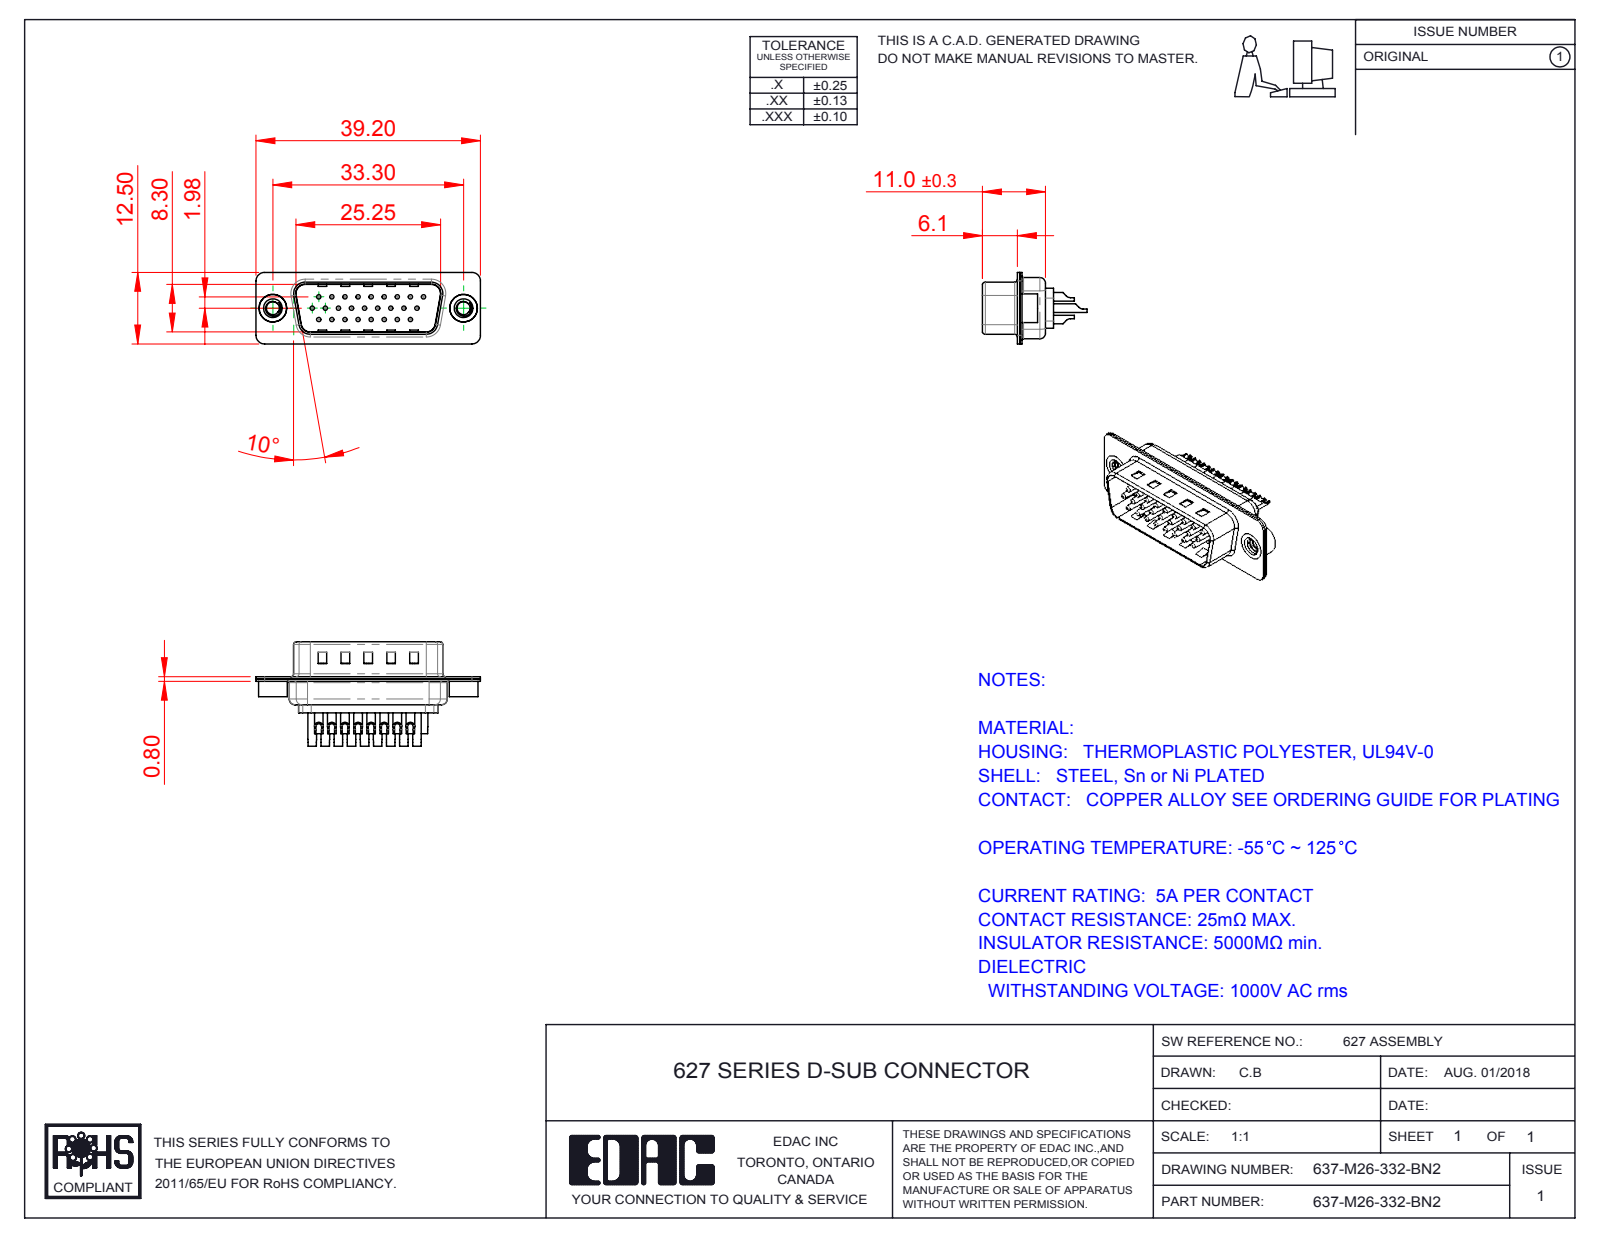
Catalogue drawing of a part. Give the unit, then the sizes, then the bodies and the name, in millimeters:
Units: millimetres
Overall size (bounding box): 39.2 × 18.25 × 12.5
Round holes (diameter × count): ⌀0.75 ×26, ⌀1 ×26, ⌀1.6 ×26, ⌀2 ×26, ⌀2.26 ×2, ⌀4 ×2, ⌀4.8 ×2
Round bosses / shafts (diameter × count): ⌀1.5 ×26, ⌀5 ×2, ⌀4.9 ×2
Partial cylindrical surfaces — rounded edges, fillets, slot ends (radius × count): R1.5 ×16, R2 ×12, R0.5 ×8, R1.6 ×8, R1 ×7, R0.25 ×4, R0.6 ×4, R0.65 ×4
Main face-to-face distances: 0.4, 0.8, 9.5, 9.1, 8.7, 9.9, 0.75, 0.35, 1.2, 1.1
Hole centre spacings: 3.96, 2.28, 4.57, 6.05, 2.29, 8.24, 6.86, 10.48
Volume: 1 996 mm³ · Surface area: 6 073 mm²
Bodies: 31 solids, 1302 faces (373 planar, 549 cylindrical, 380 other)
Part name (STEP PRODUCT): 637M Shell Rear_26 Contacts; 637M Shell Front_26 Contacts; 637M Contact Row 1_32; 637-M26-332-BN2 (+4 more)
STEP written by: SolidWorks 2016 (CONFIG_CONTROL_DESIGN)
